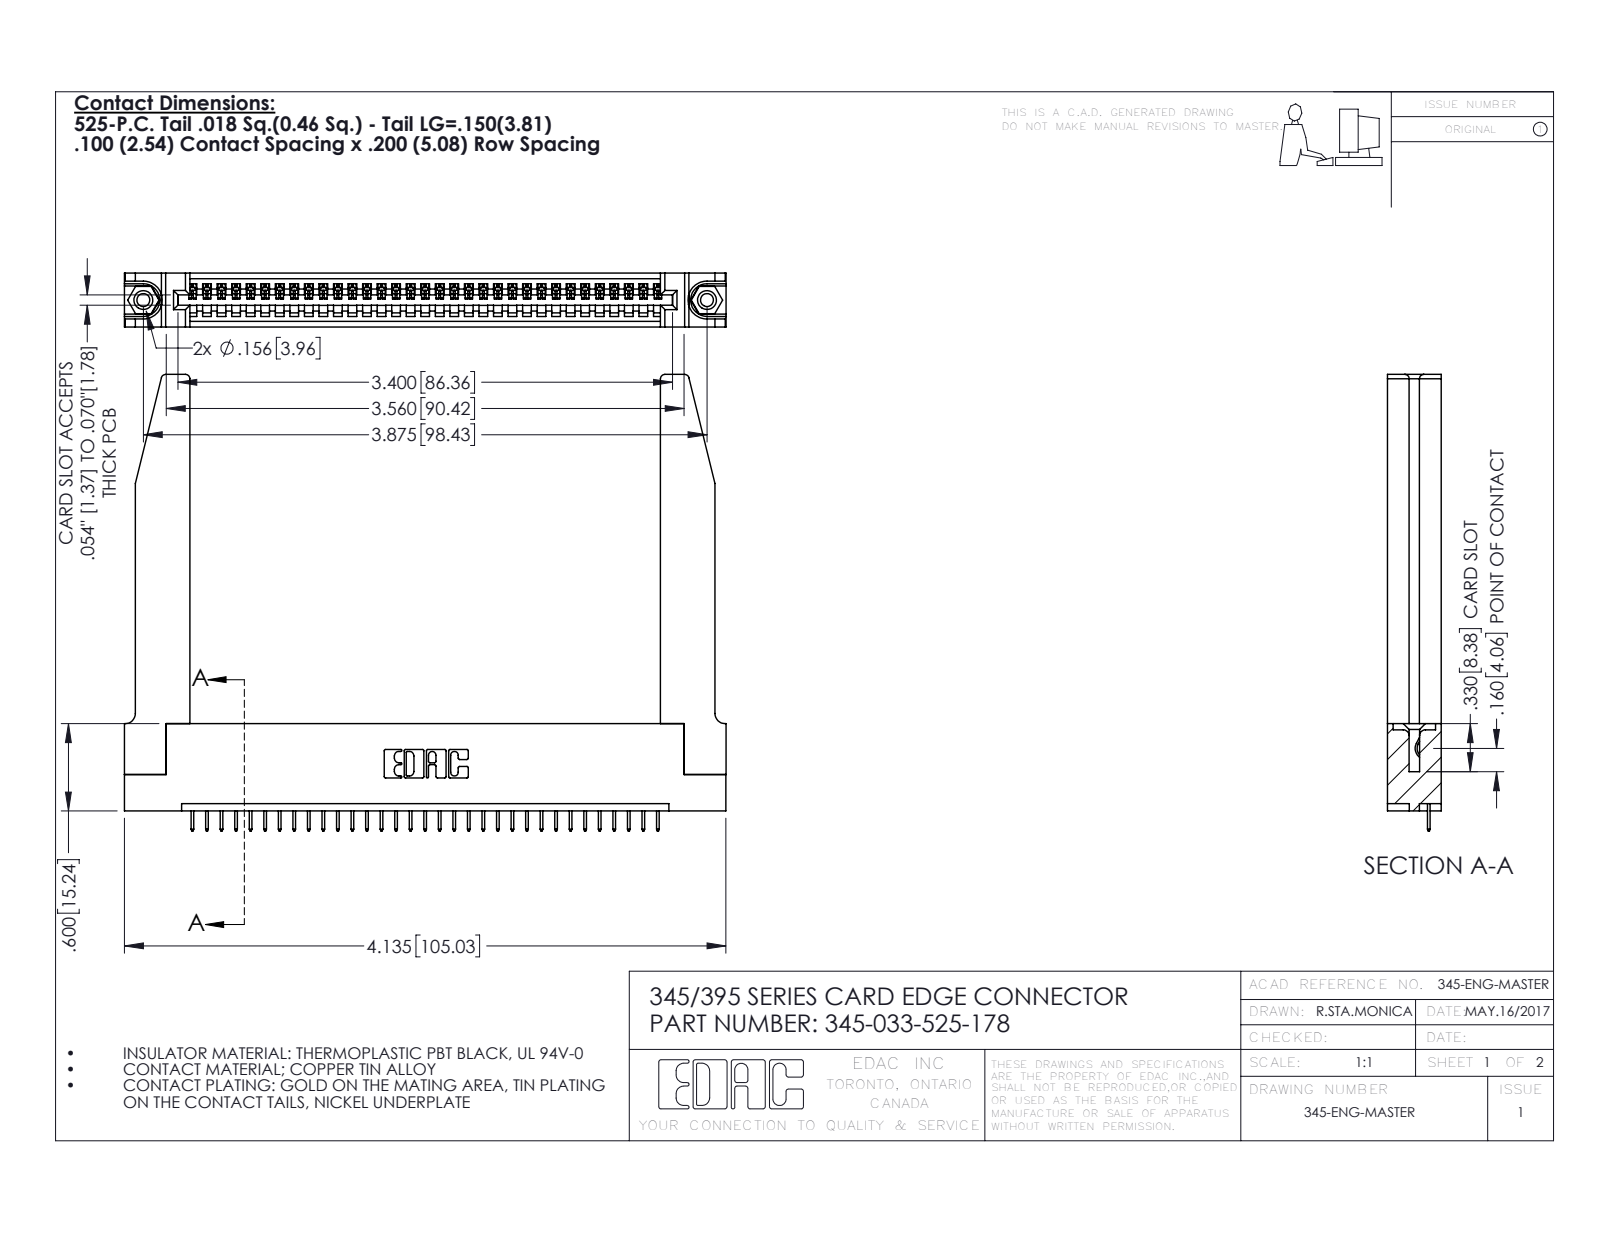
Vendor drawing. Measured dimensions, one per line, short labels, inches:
name: 345-292-001_345-293-125; 345-250-001_345-250-001-102; 345-220-078_345-220-078; 345-033-525-178 (+1 more)
written by: SolidWorks 2020 (CONFIG_CONTROL_DESIGN)
unit: in
bodies: 38 solids, 2406 faces (1740 planar, 614 cylindrical, 52 other)
size: 4.136 × 3.137 × 0.37
volume: 1.07 in³; area: 29.85 in²
holes: 2× ⌀0.089, 2× ⌀0.125, 2× ⌀0.156, 1× ⌀0.064
bosses: 2× ⌀0.155
rounds: 66× R0.006, 22× R0.01, 8× R0.03, 6× R0.007, 6× R0.031, 3× R0.026, 2× R0.031, 2× R0.04
face distances: 0.37, 0.072, 0.298, 0.2, 0.098, 0.272, 0.025, 0.148, 0.15, 0.225
hole spacings: 0.27, 3.64, 3.875
